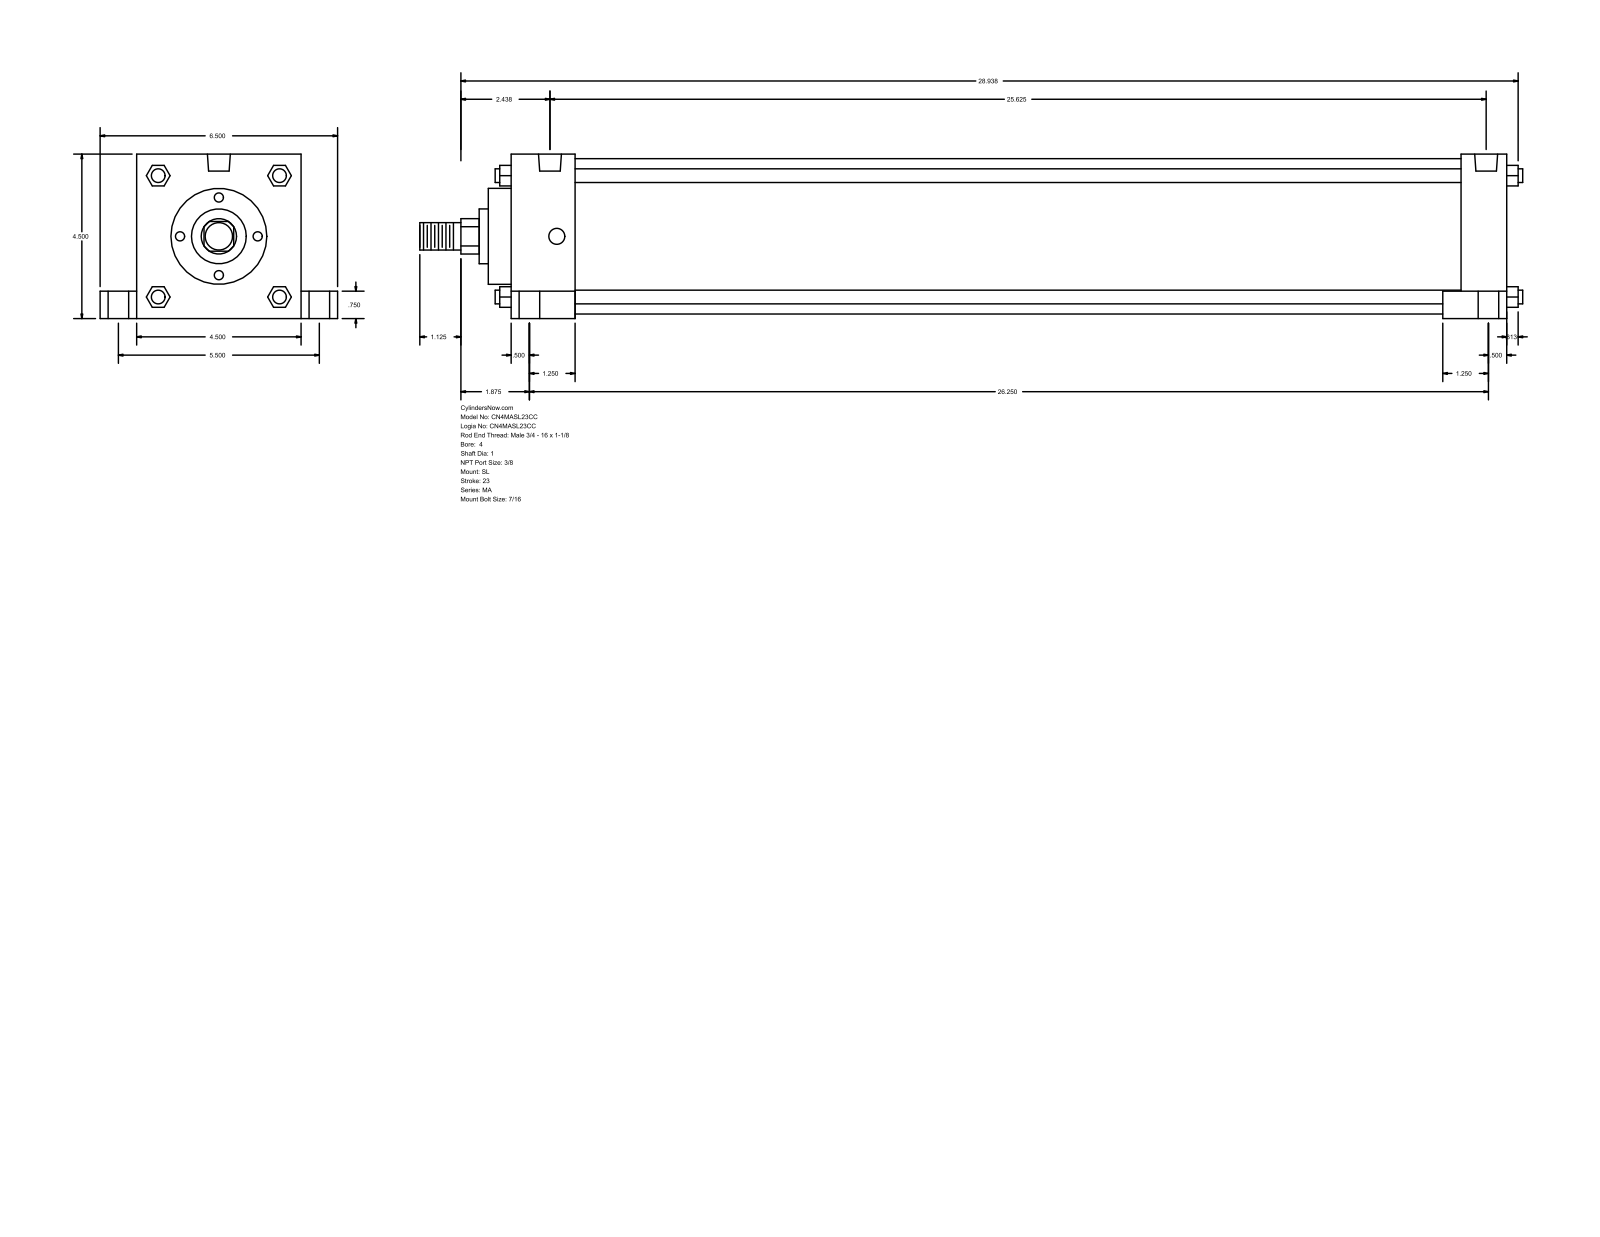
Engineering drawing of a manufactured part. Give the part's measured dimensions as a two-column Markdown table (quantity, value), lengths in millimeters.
| quantity | value |
| --- | --- |
| part name | MA_SL__0400_1 |
| STEP written by | GSSL Pune (CONFIG_CONTROL_DESIGN) |
| units | millimeters |
| bodies | 0 solids, 150 faces (113 planar, 37 cylindrical, 0 other) |
| overall size | 766.76 × 165.1 × 114.3 |
| round holes (diameter × count) | 11.11 × 4, 14.29 × 4, 20.64 × 4, 15.93 × 2 |
| round bosses / shafts (diameter × count) | 9.53 × 4, 107.95 × 1, 66.67 × 1, 38.1 × 1, 25.4 × 1, 19.05 × 1 |
| partial cylindrical surfaces (radius × count) | 12.29 × 1 |
| main face-to-face distances | 114.3, 692.16, 615.95, 44.46, 647.7, 660.41, 31.75, 25.4, 139.7, 19.05 |
| hole center spacings | 69.87, 70.14, 71.3, 72.4, 139.7, 641.35, 651.47, 656.2 |
